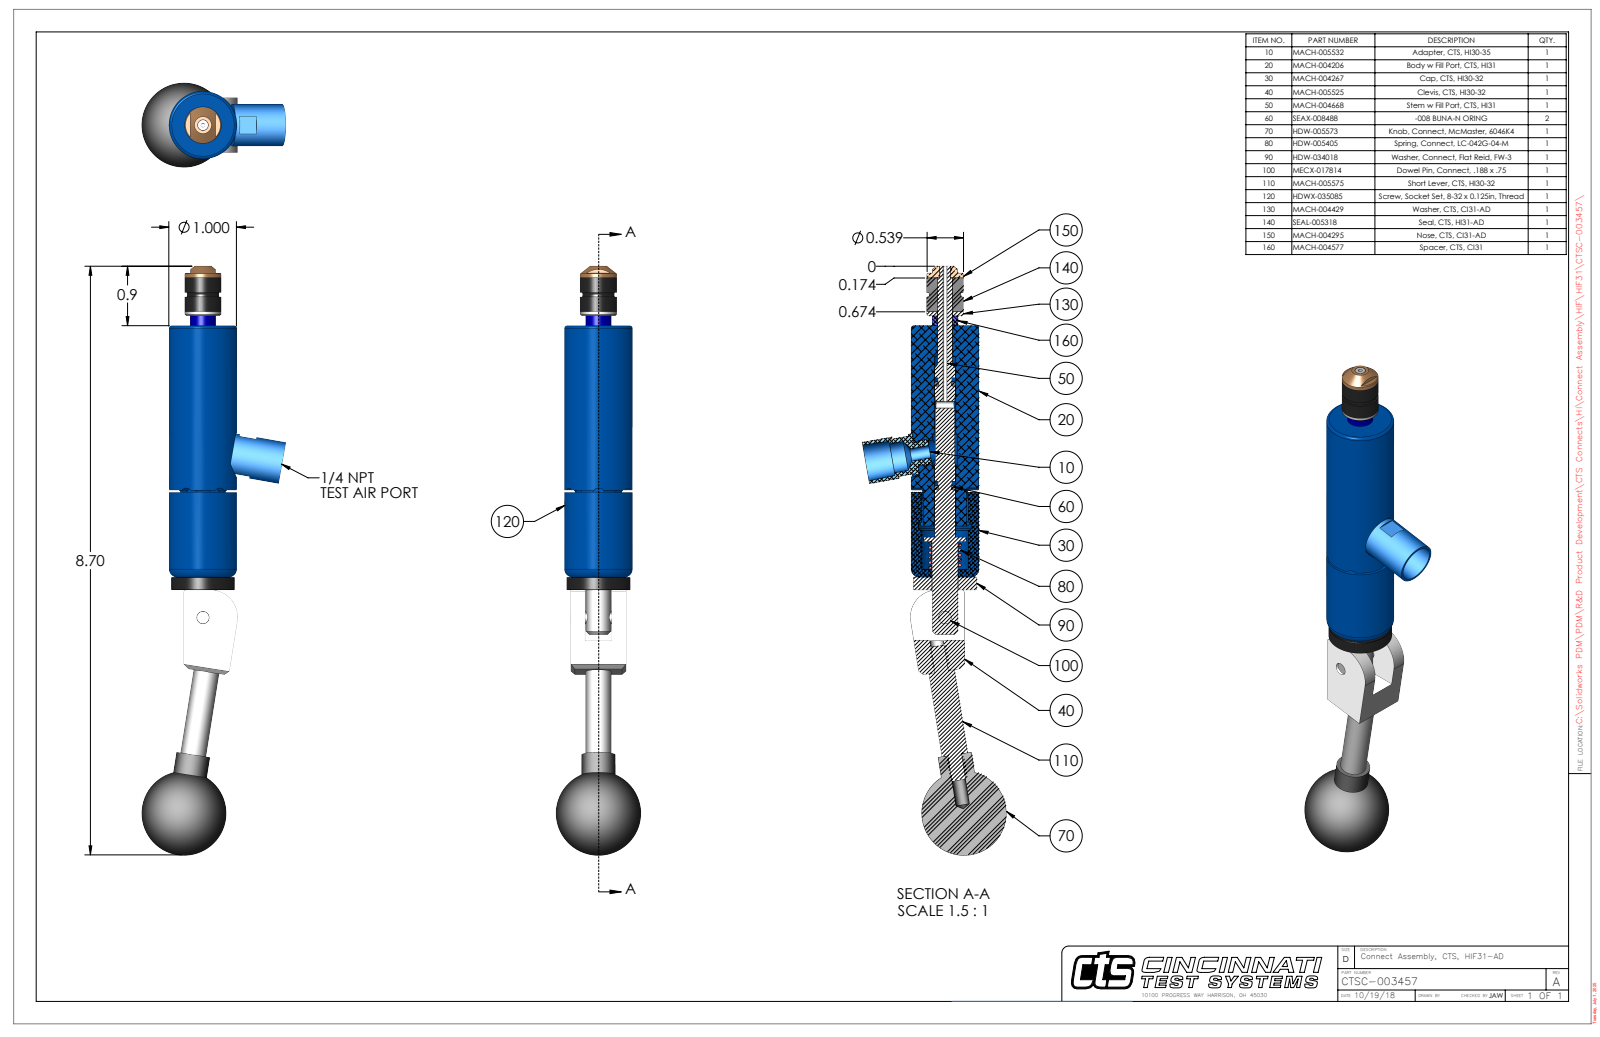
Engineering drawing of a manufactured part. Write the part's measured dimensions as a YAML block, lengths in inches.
part_name: "CTSC-003457"
step_written_by: "SolidWorks 2023 (AUTOMOTIVE_DESIGN)"
units: inches
bodies: {solids: 10, faces: 283, planar: 98, cylindrical: 121, other: 64}
overall_size: [8.704, 2.128, 1.25]
volume: 5.031
surface_area: 38.79
round_holes:
  - {diameter: 0.201, count: 2}
  - {diameter: 0.063, count: 1}
  - {diameter: 0.104, count: 1}
  - {diameter: 0.109, count: 1}
  - {diameter: 0.136, count: 1}
  - {diameter: 0.15, count: 1}
  - {diameter: 0.159, count: 1}
  - {diameter: 0.187, count: 1}
  - {diameter: 0.189, count: 1}
  - {diameter: 0.218, count: 1}
  - {diameter: 0.228, count: 1}
  - {diameter: 0.229, count: 1}
round_bosses_or_shafts:
  - {diameter: 1, count: 1}
  - {diameter: 0.936, count: 1}
  - {diameter: 0.62, count: 1}
  - {diameter: 0.541, count: 1}
  - {diameter: 0.539, count: 1}
  - {diameter: 0.5, count: 1}
  - {diameter: 0.38, count: 1}
  - {diameter: 0.379, count: 1}
partial_cylinders:
  - {radius: 0.093, count: 6}
  - {radius: 0.029, count: 2}
  - {radius: 0.325, count: 1}
  - {radius: 0.4, count: 1}
  - {radius: 0.461, count: 1}
face_to_face_distances: [0.21, 0.602, 0.812, 0.187, 3.716, 3.903, 0.391, 0.705, 4.42, 4.608]
hole_center_spacings: [0.599, 1.658, 2.252]
